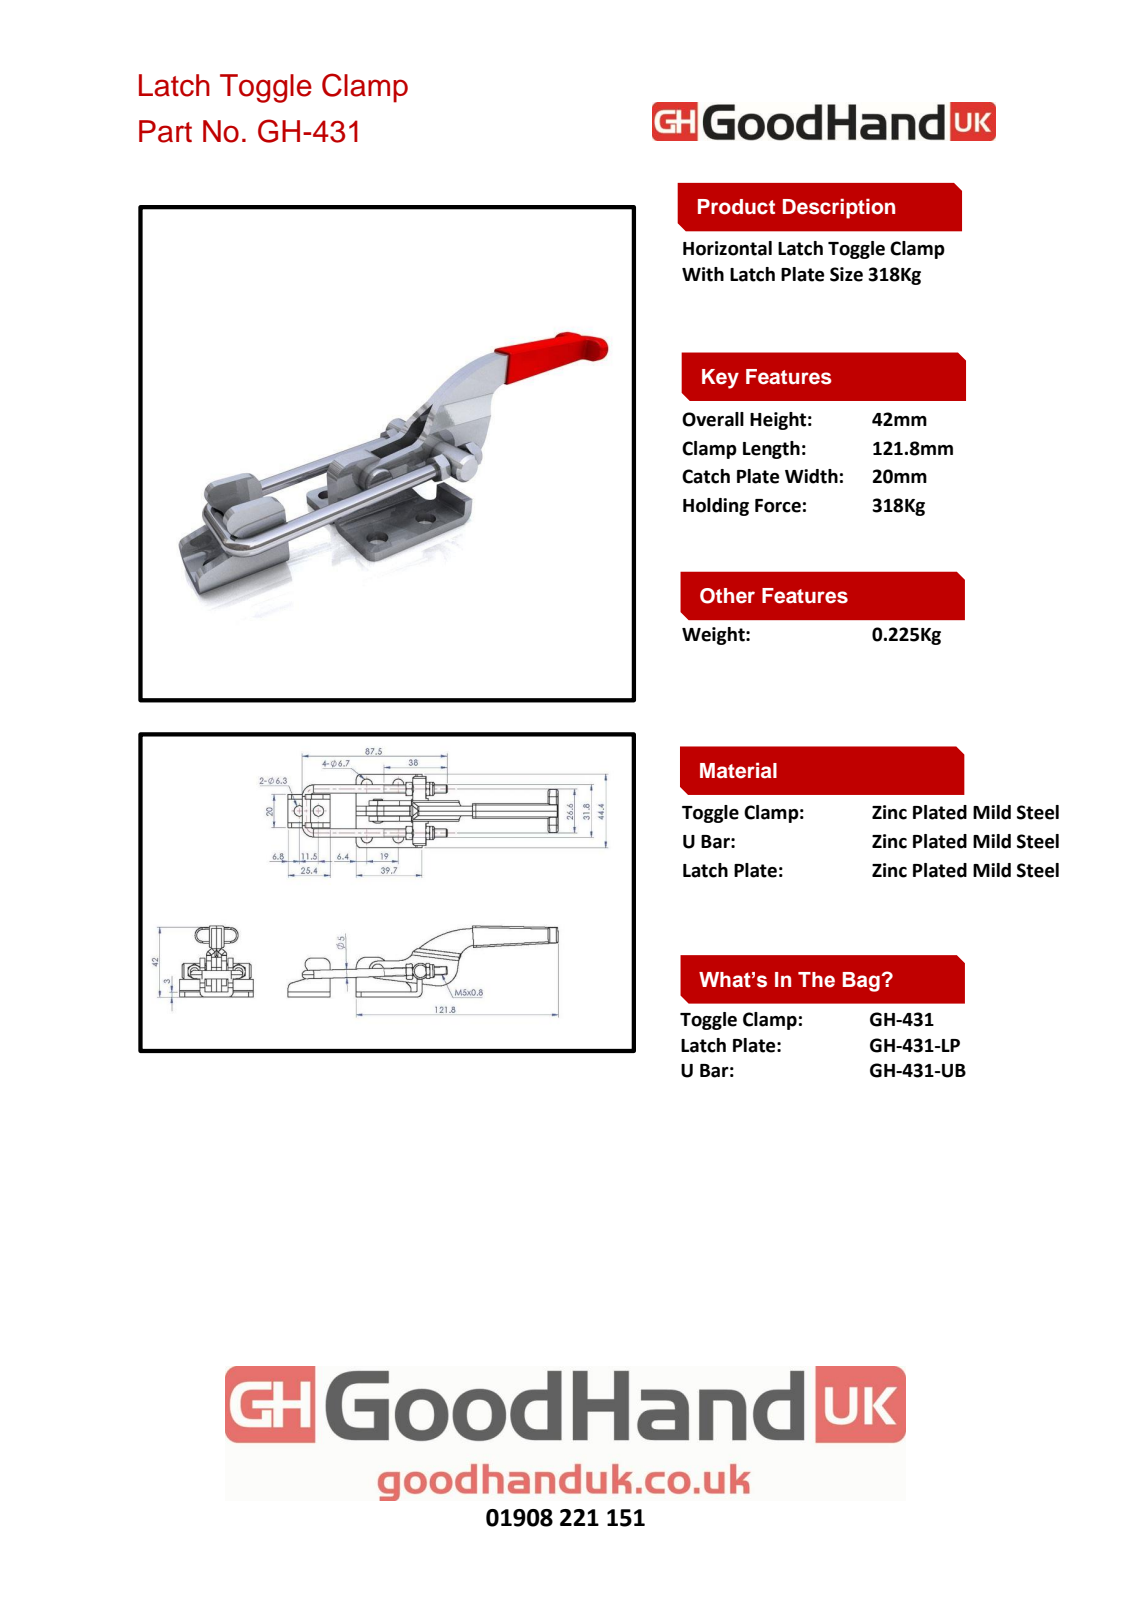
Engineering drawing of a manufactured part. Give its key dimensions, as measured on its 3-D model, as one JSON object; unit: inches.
{"part_name": "Group4^493797(GH-431); 493797(GH-431); Group3^493797(GH-431); Group1^493797(GH-431) (+1 more)", "step_written_by": "SolidWorks 2016 (AUTOMOTIVE_DESIGN)", "units": "inches", "bodies": {"solids": 6, "faces": 300, "planar": 127, "cylindrical": 115, "other": 58}, "overall_size": [6.015, 1.748, 1.689], "volume_in3": 1.934, "surface_area_in2": 33.17, "round_holes": [[0.165, 4], [0.197, 4], [0.264, 4], [0.231, 2], [0.248, 2], [0.138, 1], [0.374, 1]], "round_bosses_or_shafts": [[0.197, 3], [0.315, 2], [0.232, 1], [0.193, 1]], "partial_cylinders_radius": [[0.118, 4], [0.119, 4], [0.453, 4], [2.06, 4], [0.079, 2], [0.181, 2], [0.236, 2], [0.039, 1]], "face_to_face_distances": [0.118, 0.24, 0.122, 0.358, 0.362, 0.055, 0.417, 0.063, 0.059, 0.295], "hole_center_spacings": [1.047, 0.748, 1.252, 1.458, 0.453, 0.954, 0.996, 1.016]}
